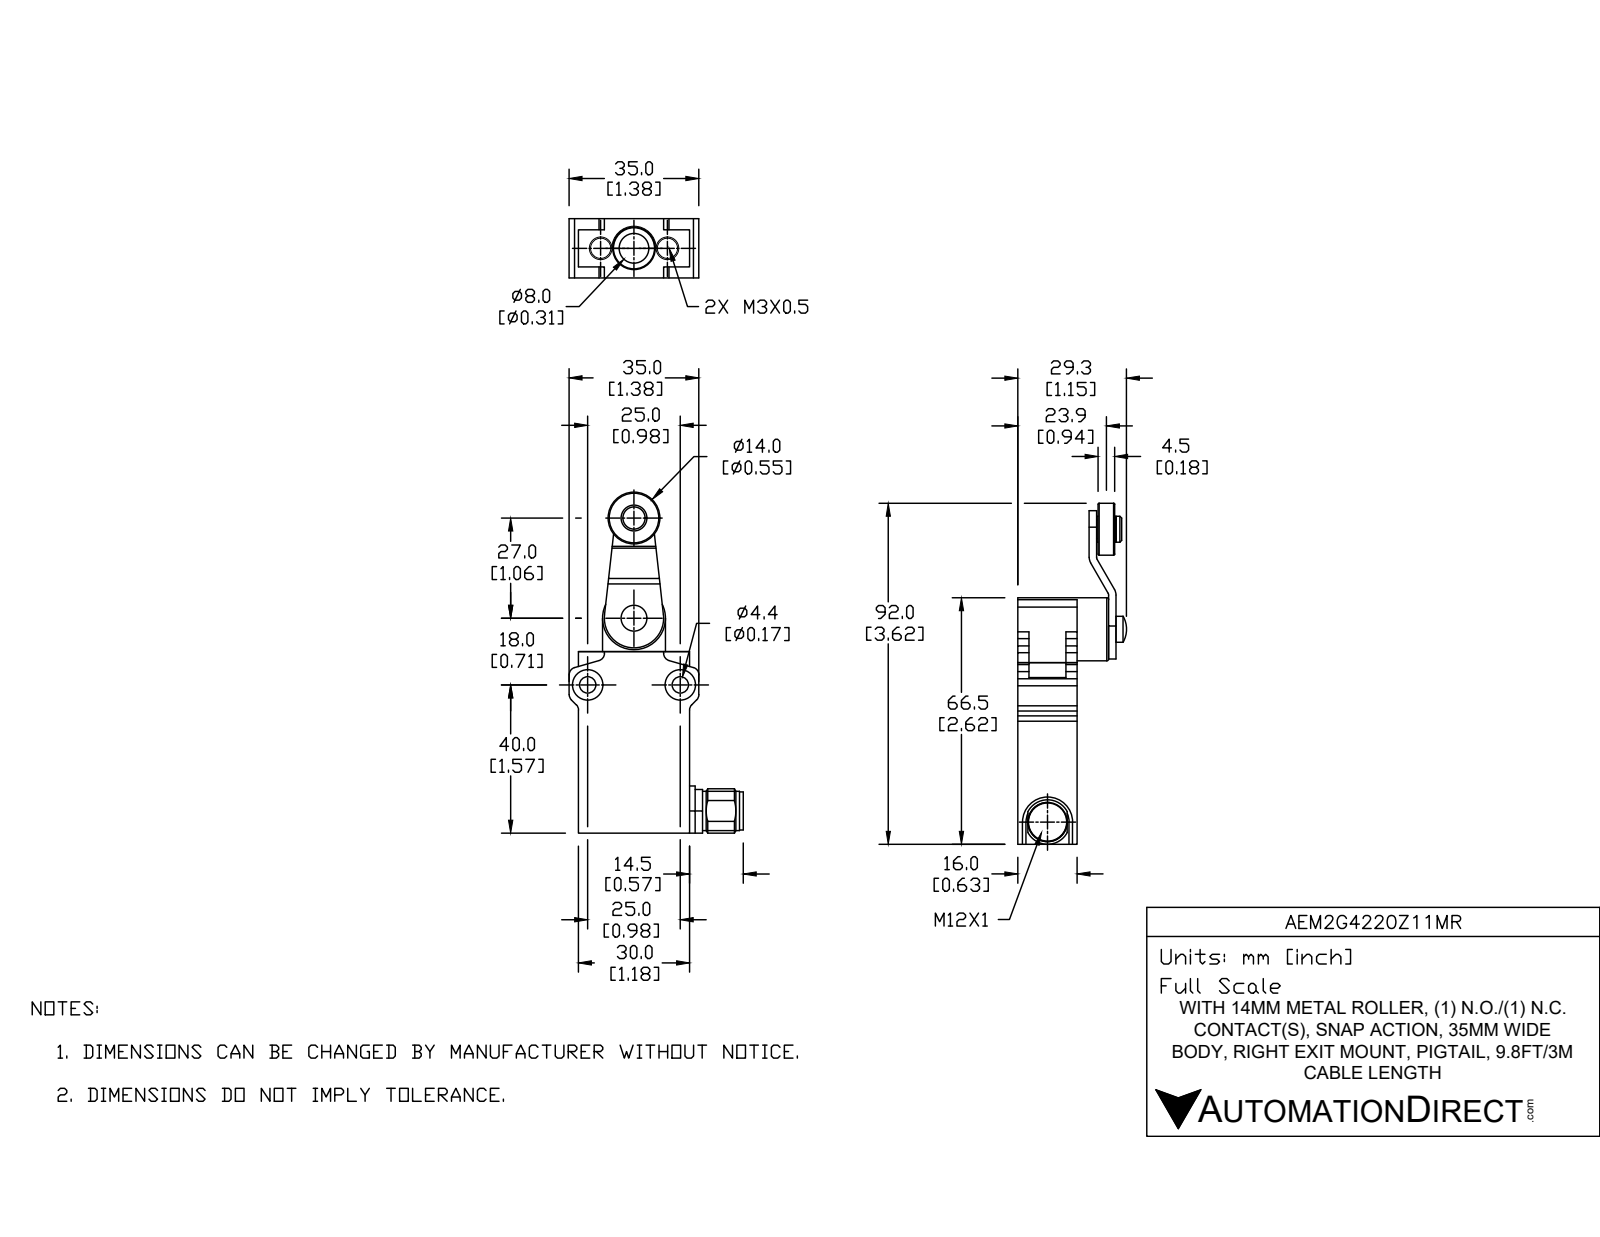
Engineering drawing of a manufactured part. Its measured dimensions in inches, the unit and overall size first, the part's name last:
Units: inches
Overall size (bounding box): 3.72 × 1.831 × 1.26
Round holes (diameter × count): ⌀0.118 ×2, ⌀0.173 ×2, ⌀0.323 ×2, ⌀0.098 ×1, ⌀0.161 ×1, ⌀0.197 ×1, ⌀0.224 ×1
Round bosses / shafts (diameter × count): ⌀0.276 ×2, ⌀0.622 ×1, ⌀0.551 ×1, ⌀0.472 ×1, ⌀0.417 ×1, ⌀0.406 ×1, ⌀0.394 ×1, ⌀0.236 ×1
Partial cylindrical surfaces — rounded edges, fillets, slot ends (radius × count): R0.079 ×8, R0.039 ×2, R0.118 ×2, R0.256 ×1, R0.315 ×1
Main face-to-face distances: 0.63, 1.181, 2.047, 0.354, 0.079, 0.984, 0.28, 0.902, 0.102, 0.472
Hole centre spacings: 0.863, 1.82, 0.748, 0.984, 1.043
Volume: 1.995 in³ · Surface area: 18.48 in²
Bodies: 7 solids, 545 faces (299 planar, 61 cylindrical, 185 other)
Part name (STEP PRODUCT): AEM2G4220Z11MR
STEP written by: SolidWorks 2019 (AUTOMOTIVE_DESIGN)
